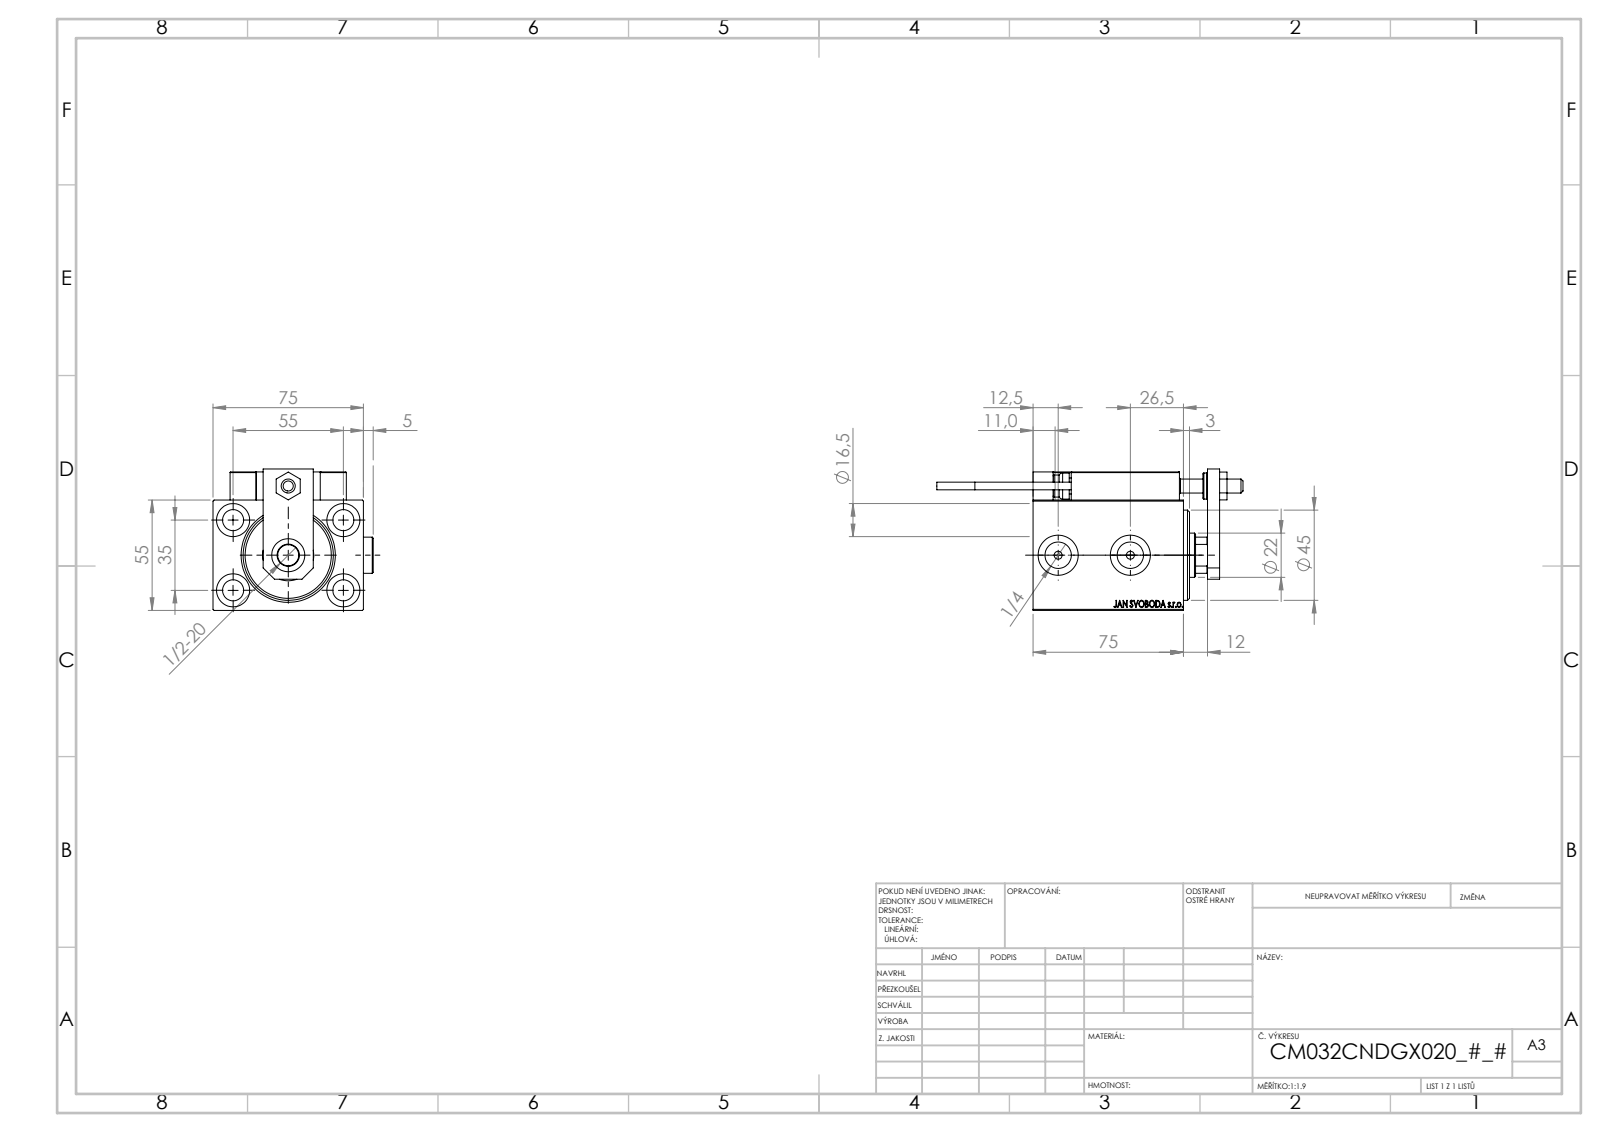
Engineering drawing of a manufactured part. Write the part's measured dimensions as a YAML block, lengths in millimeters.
part_name: "SWITCH_X_FRONT_BACK; Block; SWITCH X; ALLEN BOLT D8 (+7 more)"
step_written_by: "SolidWorks 2019 (CONFIG_CONTROL_DESIGN)"
units: millimeters
bodies: {solids: 25, faces: 1336, planar: 594, cylindrical: 204, other: 538}
overall_size: [152.7, 79.9, 70.5]
volume: 311696
surface_area: 87420
round_holes:
  - {diameter: 4, count: 6}
  - {diameter: 8, count: 5}
  - {diameter: 10.5, count: 5}
  - {diameter: 16.5, count: 5}
  - {diameter: 3.2, count: 4}
  - {diameter: 5, count: 2}
  - {diameter: 13.16, count: 2}
  - {diameter: 20, count: 2}
  - {diameter: 7, count: 1}
  - {diameter: 22, count: 1}
  - {diameter: 25.5, count: 1}
  - {diameter: 32, count: 1}
round_bosses_or_shafts:
  - {diameter: 18, count: 2}
  - {diameter: 5, count: 2}
  - {diameter: 3.8, count: 2}
  - {diameter: 13, count: 1}
  - {diameter: 11, count: 1}
partial_cylinders:
  - {radius: 0.3, count: 30}
  - {radius: 3, count: 2}
  - {radius: 10.5, count: 1}
face_to_face_distances: [55, 75, 14, 10, 12, 7, 5, 69, 25, 20]
hole_center_spacings: [32.6, 11.37, 20, 27.07, 29.59, 29.69, 32.33, 34.83]
